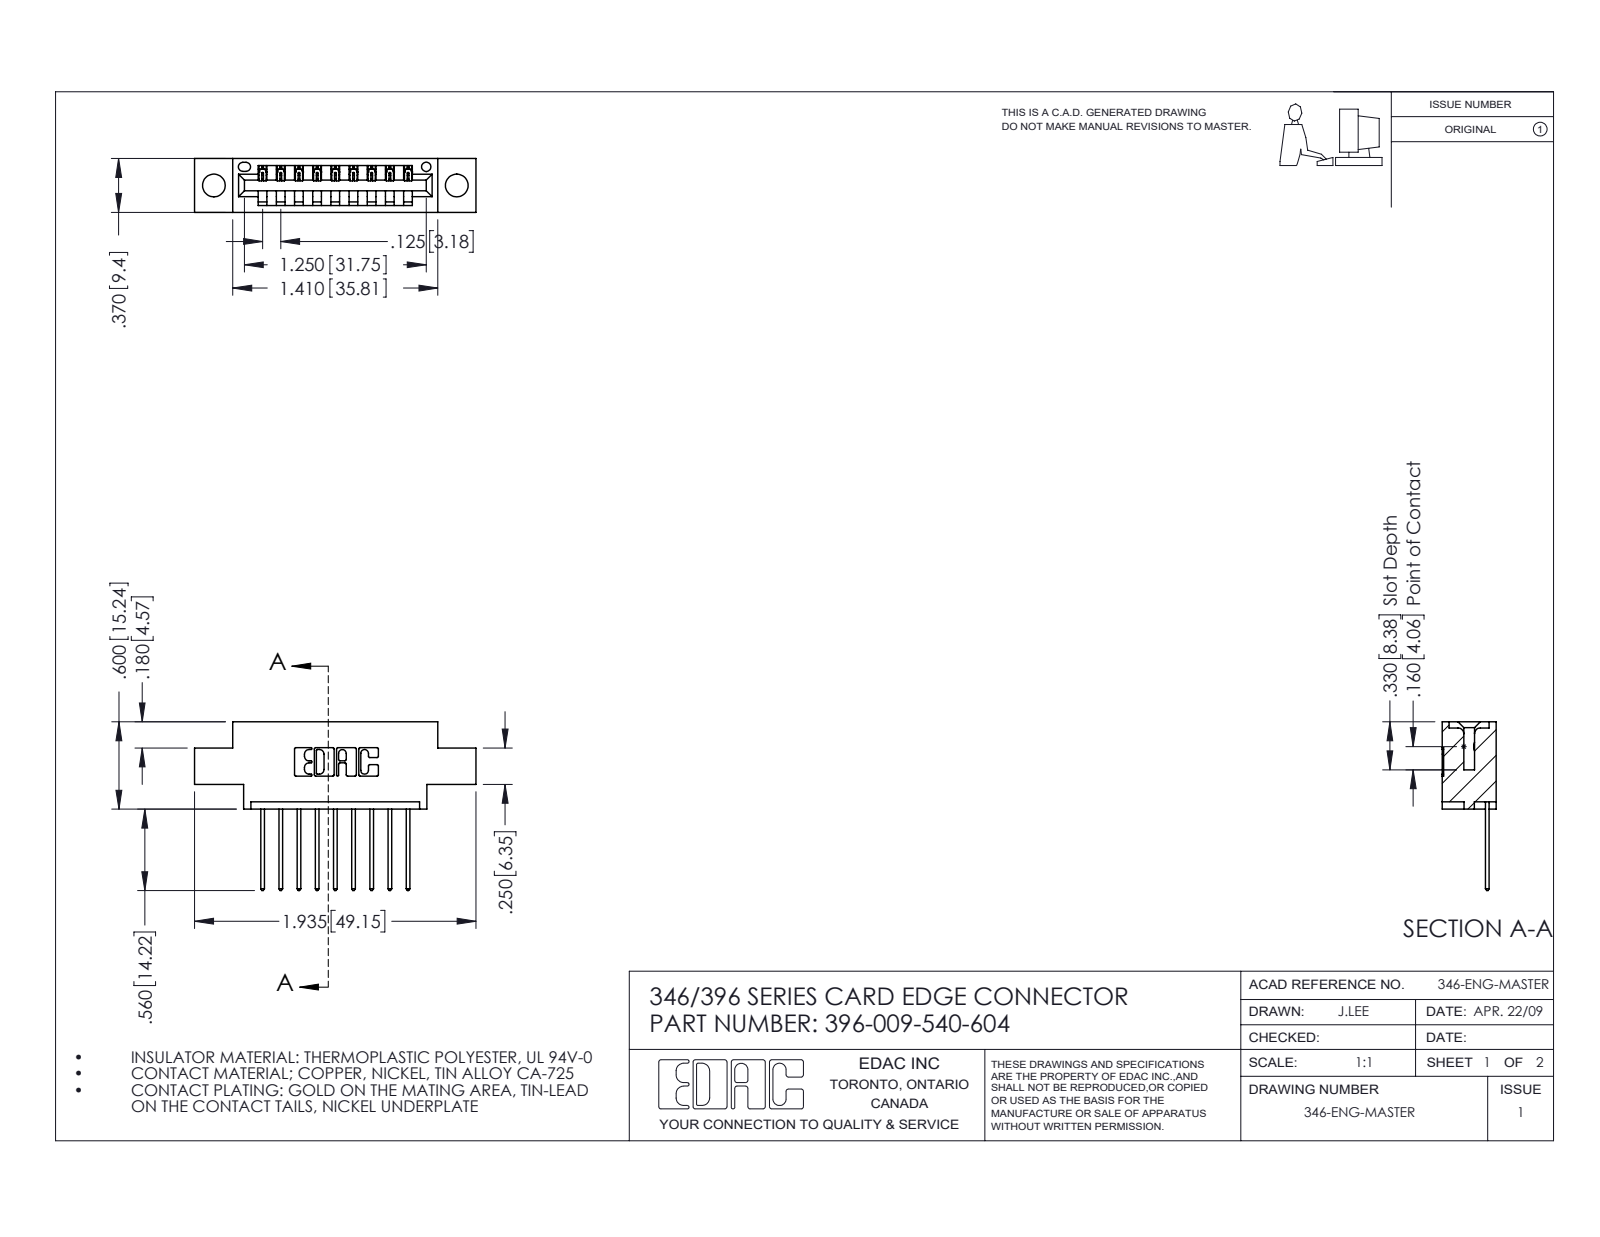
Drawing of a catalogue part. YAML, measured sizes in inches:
part_name: "396-009-540-604; 345-292-001_345-293-140; 346 Part_0.170 Offset - 0.156 Dia-TH"
step_written_by: "SolidWorks 2016 (CONFIG_CONTROL_DESIGN)"
units: inches
bodies: {solids: 10, faces: 648, planar: 440, cylindrical: 208, other: 0}
overall_size: [1.935, 1.16, 0.37]
volume: 0.259
surface_area: 7.76
round_holes:
  - {diameter: 0.156, count: 2}
  - {diameter: 0.064, count: 1}
partial_cylinders:
  - {radius: 0.01, count: 22}
  - {radius: 0.006, count: 18}
  - {radius: 0.01, count: 18}
  - {radius: 0.007, count: 6}
  - {radius: 0.031, count: 6}
  - {radius: 0.026, count: 3}
  - {radius: 0.031, count: 2}
  - {radius: 0.04, count: 2}
face_to_face_distances: [0.25, 0.37, 0.048, 0.322, 0.072, 0.298, 0.025, 0.148, 0.222, 0.1]
hole_center_spacings: [0.246, 1.465, 1.67]
